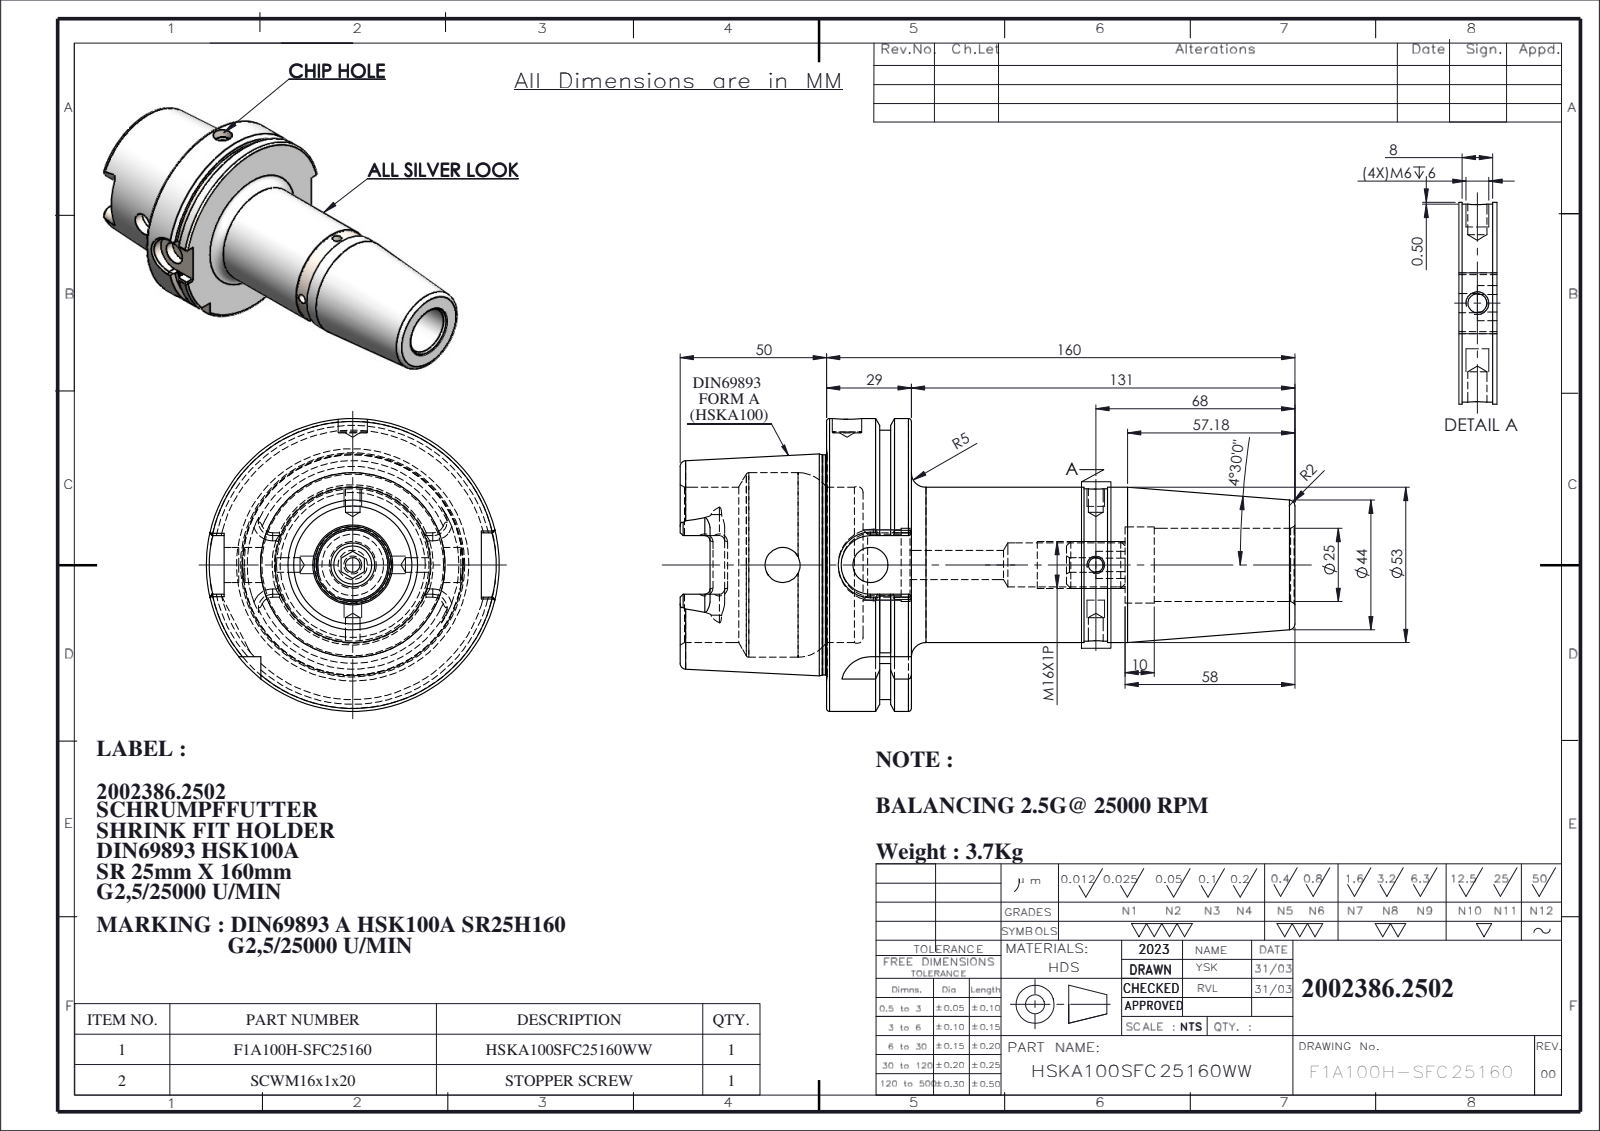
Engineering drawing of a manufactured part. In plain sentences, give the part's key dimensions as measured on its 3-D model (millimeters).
The part is named "HSKA100SFC25160WW; SCWM16X1P; 91100A-SR25160". Its 3-D file was written by "SolidWorks 2018 (CONFIG_CONTROL_DESIGN)". It is 2 solids with 222 faces: 64 planar, 70 cylindrical and 88 other. Overall it measures 209.95 by 100 by 100 millimeters. Its volume is 486 496 cubic millimeters and its surface area 79 506 square millimeters. Round holes: 3 of diameter 5, 2 of diameter 10, 2 of diameter 12, 1 of diameter 15, 1 of diameter 21, 1 of diameter 24.98, 1 of diameter 25, 1 of diameter 25.98, 1 of diameter 53, 1 of diameter 63. Round bosses or shafts: 1 of diameter 100, 1 of diameter 92, 1 of diameter 75.16, 1 of diameter 52, 1 of diameter 16. Partial cylindrical surfaces (rounded edges, fillets, slot ends): 6 of radius 1.8, 4 of radius 4.88, 2 of radius 10, 1 of radius 11. The main face-to-face distances are 28.95, 12.5, 16.45, 50, 62.5, 78.95, 209.95, 159.95, 147.45, 131. The hole center spacings are 30, 76.95, 84.95, 106.95.
